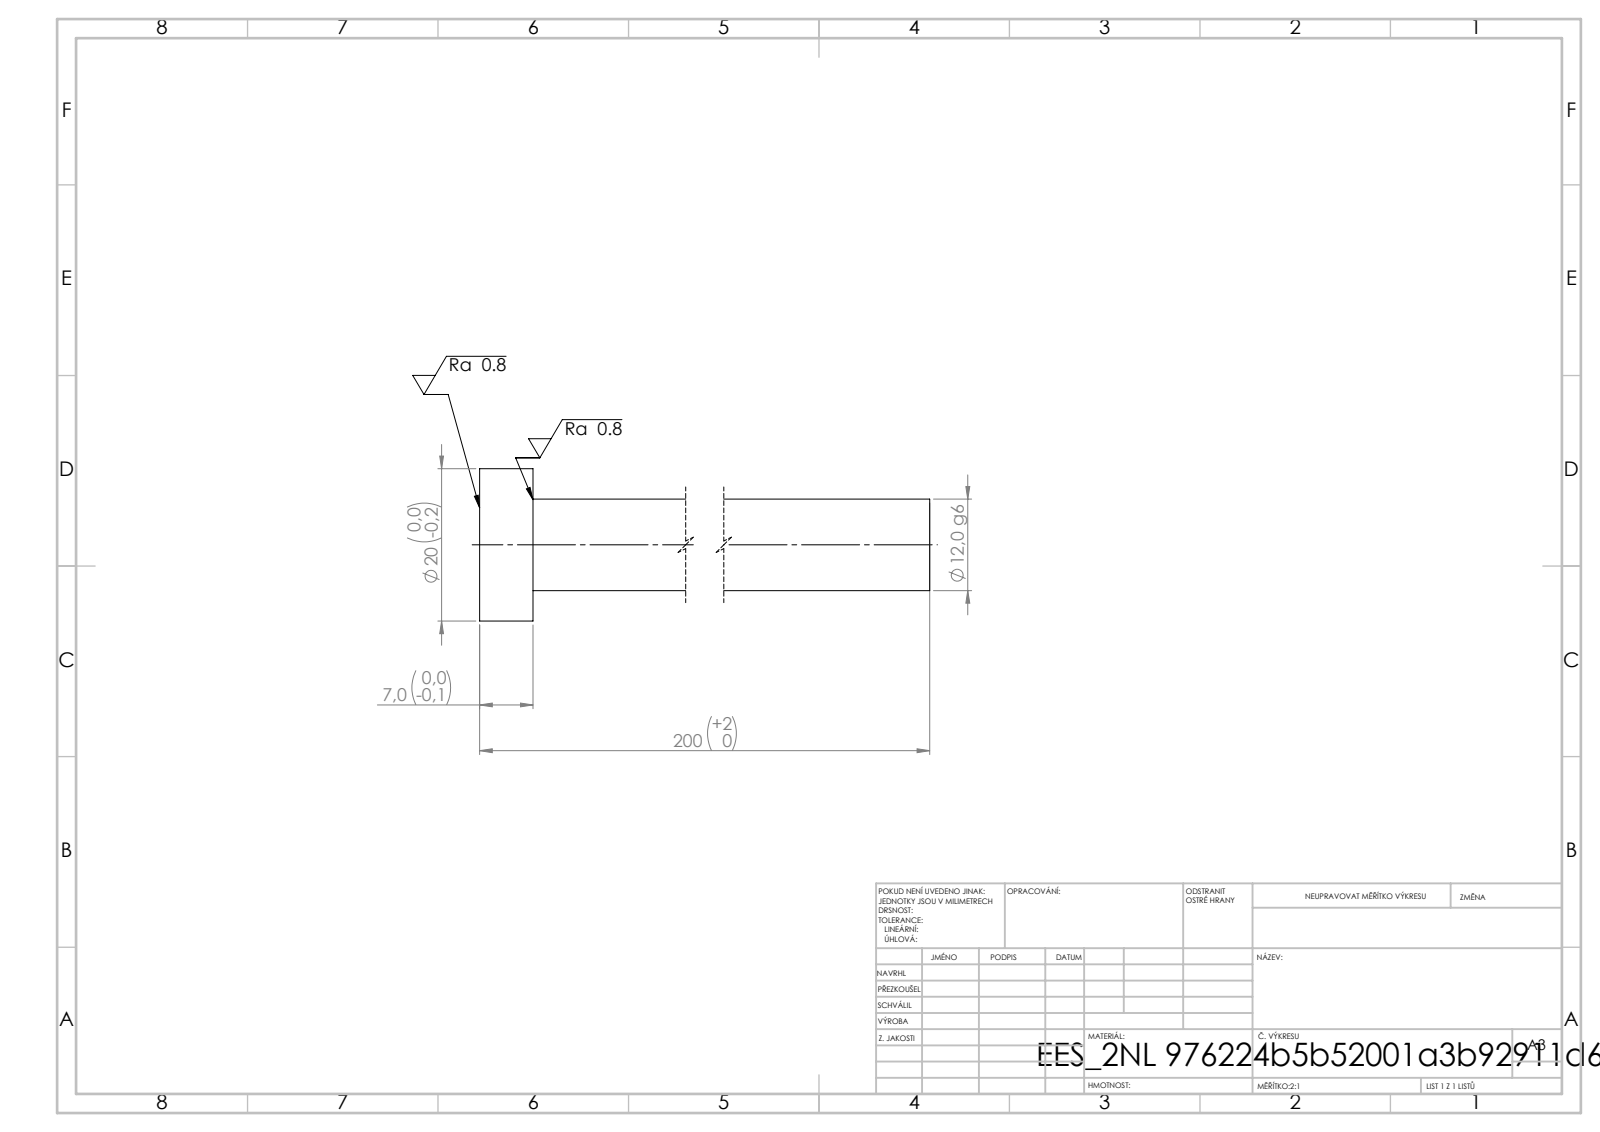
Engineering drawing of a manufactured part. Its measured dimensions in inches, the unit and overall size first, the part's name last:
Units: inches
Overall size (bounding box): 7.874 × 0.787 × 0.787
Round bosses / shafts (diameter × count): ⌀0.787 ×1, ⌀0.472 ×1
Main face-to-face distances: 0.276, 7.874, 7.598
Volume: 1.466 in³ · Surface area: 12.93 in²
Bodies: 1 solid, 7 faces (3 planar, 4 cylindrical, 0 other)
STEP written by: SolidWorks 2019 (CONFIG_CONTROL_DESIGN)
